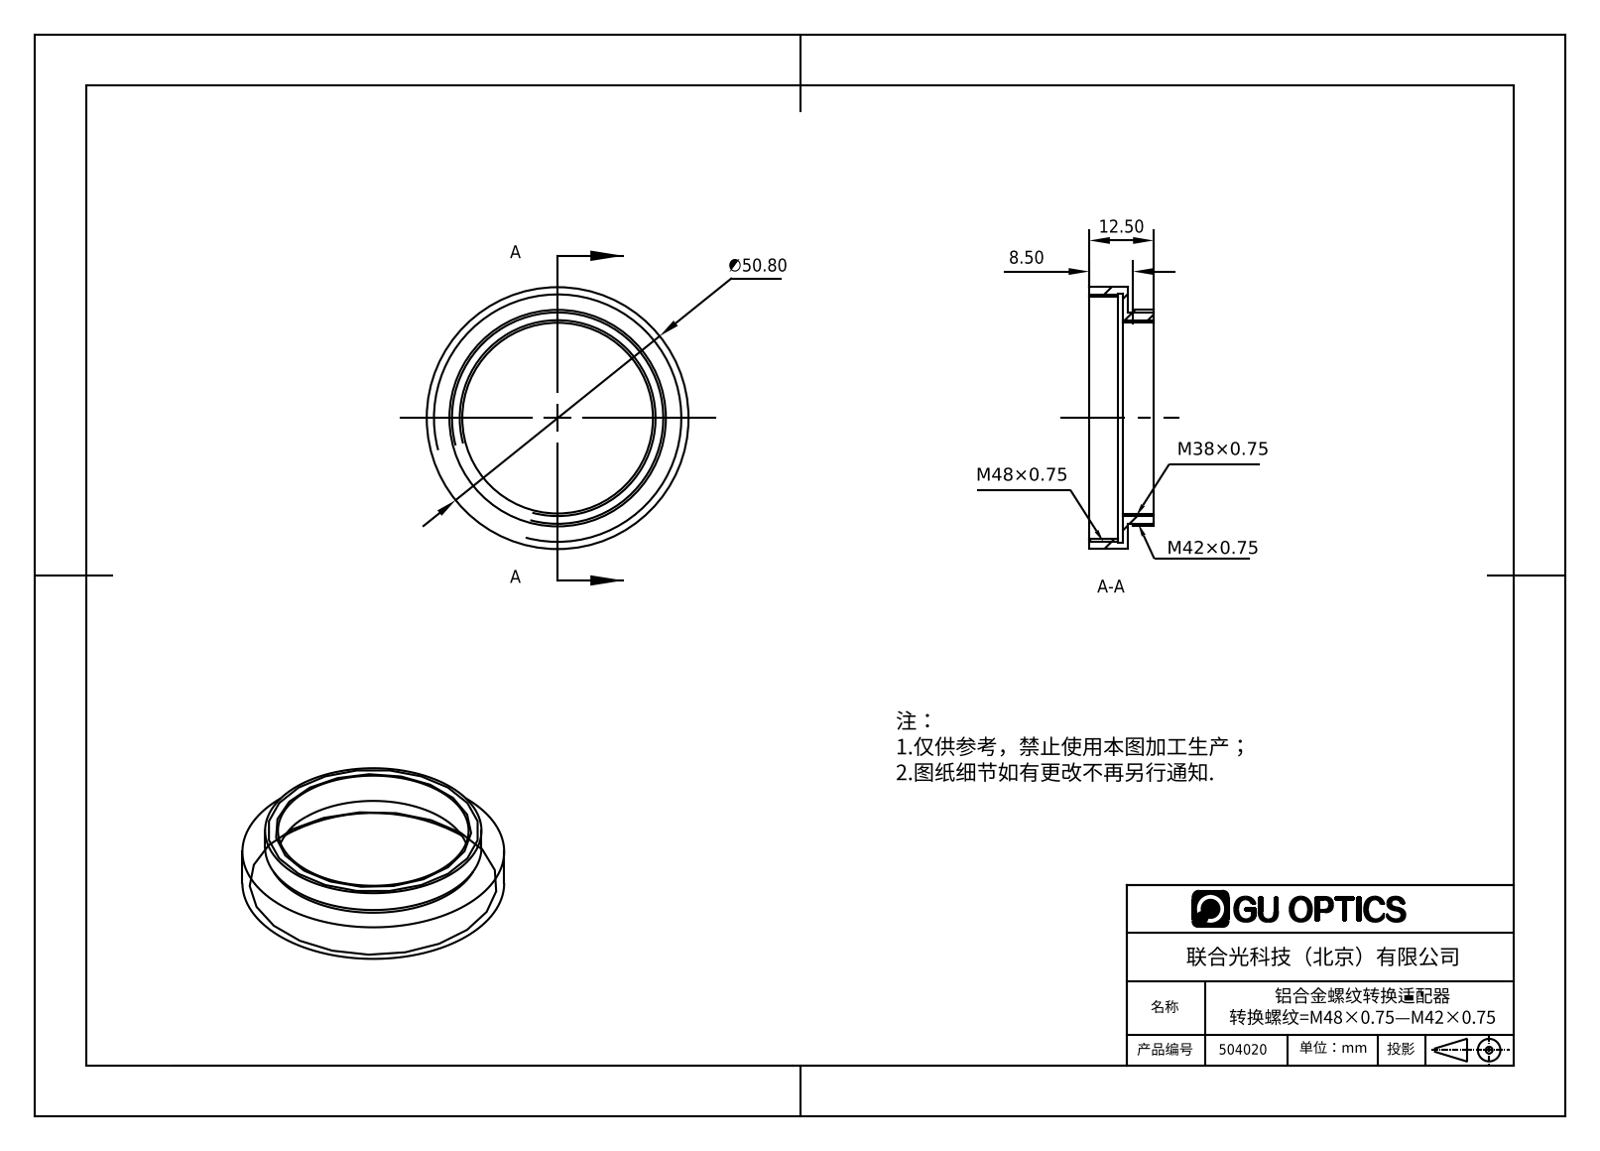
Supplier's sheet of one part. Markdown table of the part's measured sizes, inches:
| quantity | value |
| --- | --- |
| part name | 504020 |
| STEP written by | SolidWorks 2016 (AUTOMOTIVE_DESIGN) |
| units | inches |
| bodies | 1 solid, 18 faces (6 planar, 12 cylindrical, 0 other) |
| overall size | 2 × 2 × 0.492 |
| volume | 0.259 in³ |
| surface area | 8.878 in² |
| round holes (diameter × count) | 1.457 × 1, 1.85 × 1, 1.898 × 1 |
| round bosses / shafts (diameter × count) | 2 × 1, 1.654 × 1, 1.614 × 1 |
| main face-to-face distances | 0.039, 0.236, 0.197, 0.256, 0.295, 0.492, 0.079, 0.217, 0.276, 0.335 |
